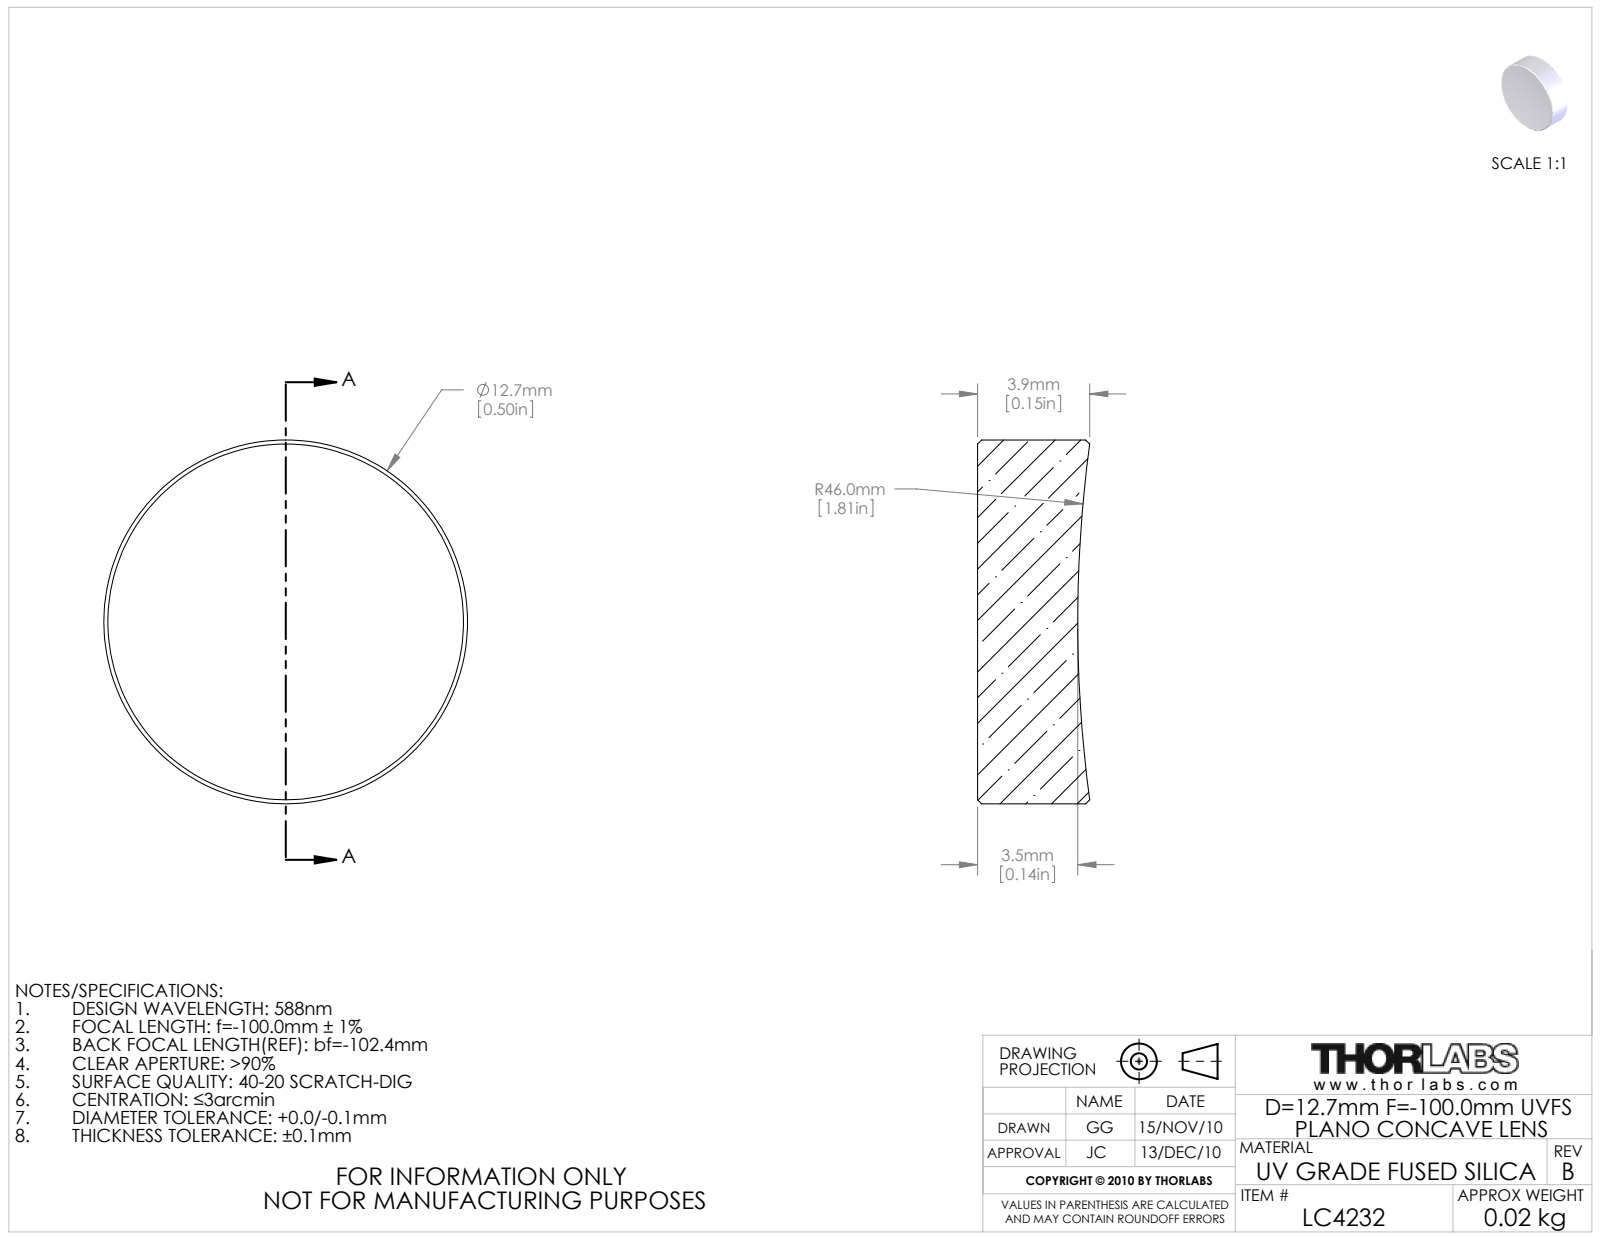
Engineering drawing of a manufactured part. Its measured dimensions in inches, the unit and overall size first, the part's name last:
Units: inches
Overall size (bounding box): 0.5 × 0.5 × 0.154
Round bosses / shafts (diameter × count): ⌀0.5 ×1
Volume: 0.029 in³ · Surface area: 0.626 in²
Bodies: 1 solid, 9 faces (1 planar, 2 cylindrical, 6 other)
Part name (STEP PRODUCT): 3499-E0W
STEP written by: SolidWorks 2009 (AUTOMOTIVE_DESIGN)
